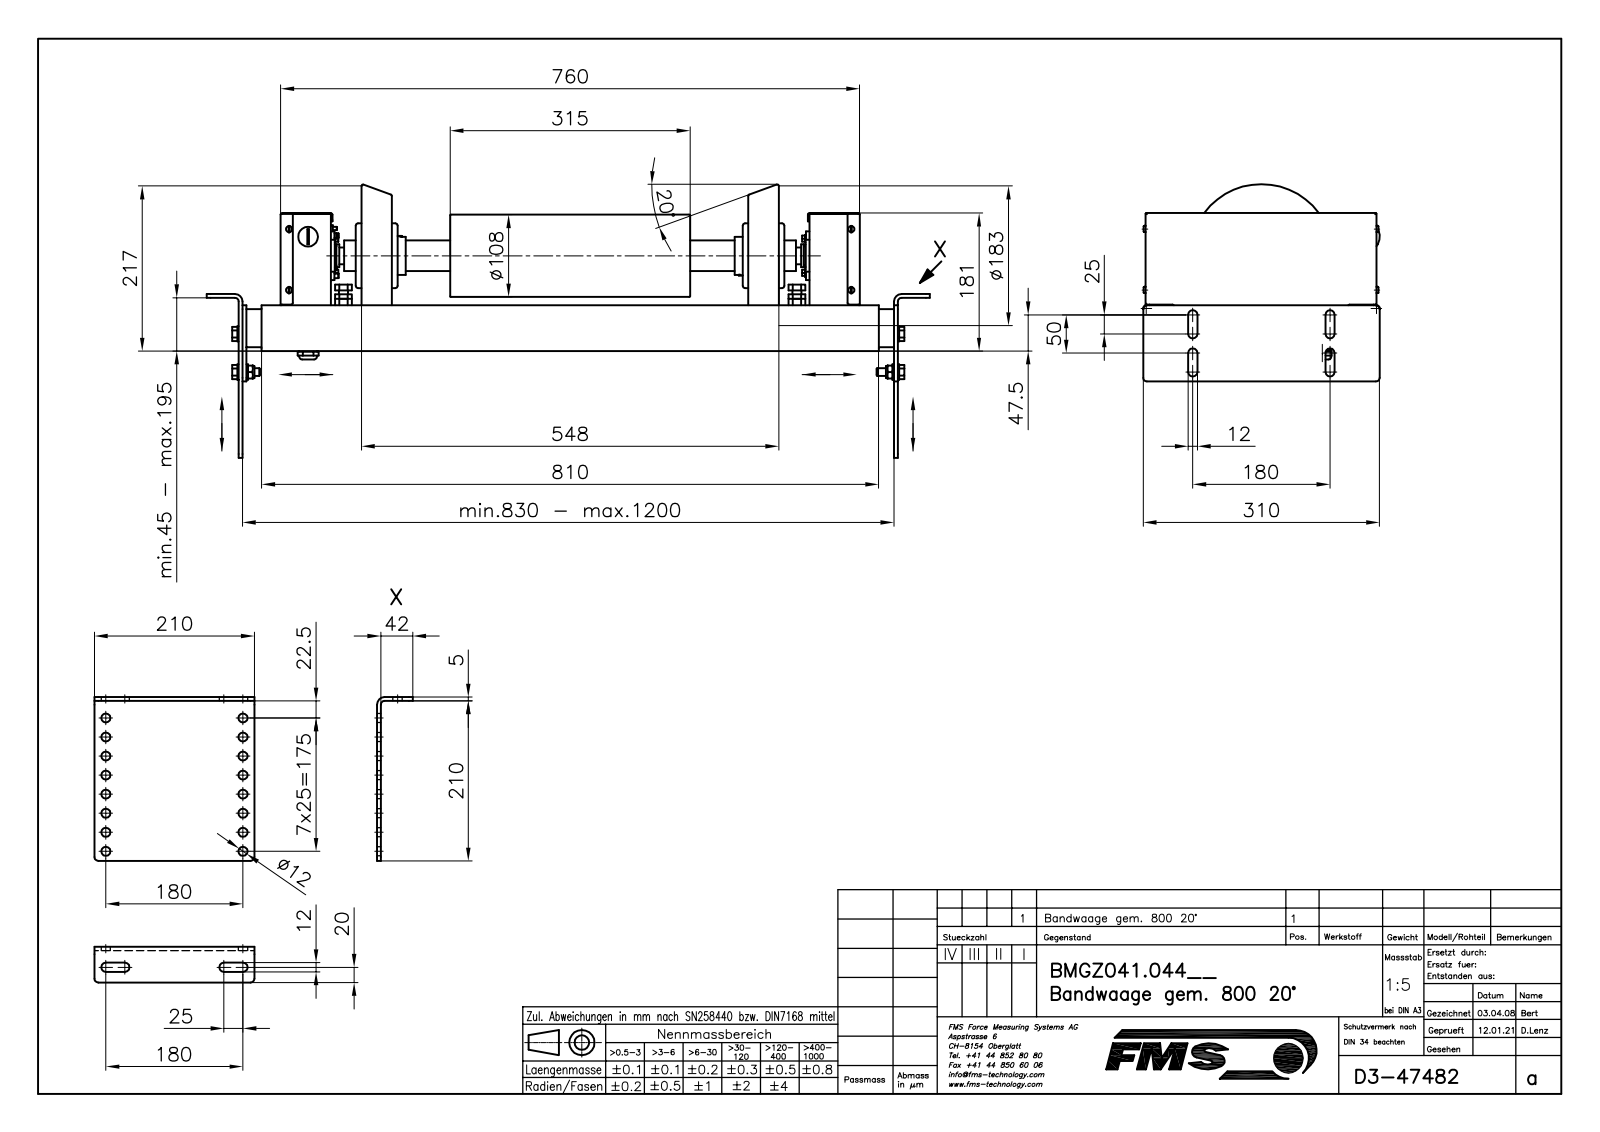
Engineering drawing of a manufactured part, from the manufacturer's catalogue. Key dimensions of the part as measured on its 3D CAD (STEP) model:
Part name (STEP PRODUCT): B47482_STP; B50030; 6KT-SCHRAUBE_M12X30; ZYL_SCHR__M4X8 (+8 more)
STEP written by: Mechanical Desktop 2009 (CONFIG_CONTROL_DESIGN)
Units: millimetres
Bodies: 156 solids, 2658 faces (1351 planar, 944 cylindrical, 363 other)
Overall size (bounding box): 949 × 358.7 × 310.2
Volume: 7 724 000 mm³ · Surface area: 2 613 000 mm²
Round holes (diameter × count): ⌀12 ×17, ⌀5 ×6, ⌀3.5 ×4, ⌀4.9 ×4, ⌀6.4 ×4, ⌀8.68 ×4, ⌀8.75 ×4, ⌀10 ×4, ⌀10.5 ×4, ⌀10.68 ×4, ⌀14.8 ×4, ⌀6 ×3
Round bosses / shafts (diameter × count): ⌀12 ×11, ⌀8.2 ×8, ⌀4.2 ×8, ⌀20 ×6, ⌀10 ×6, ⌀5 ×5, ⌀16 ×4, ⌀11.1 ×4
Partial cylindrical surfaces — rounded edges, fillets, slot ends (radius × count): R2 ×34, R1 ×24, R4 ×16, R5 ×16, R6 ×14, R3.5 ×8, R2.25 ×6, R0.5 ×4
Main face-to-face distances: 4, 5, 1, 51, 36, 270, 46, 50, 3, 56
Hole centre spacings: 25, 181.73, 50, 186.82, 75, 195, 100, 180
